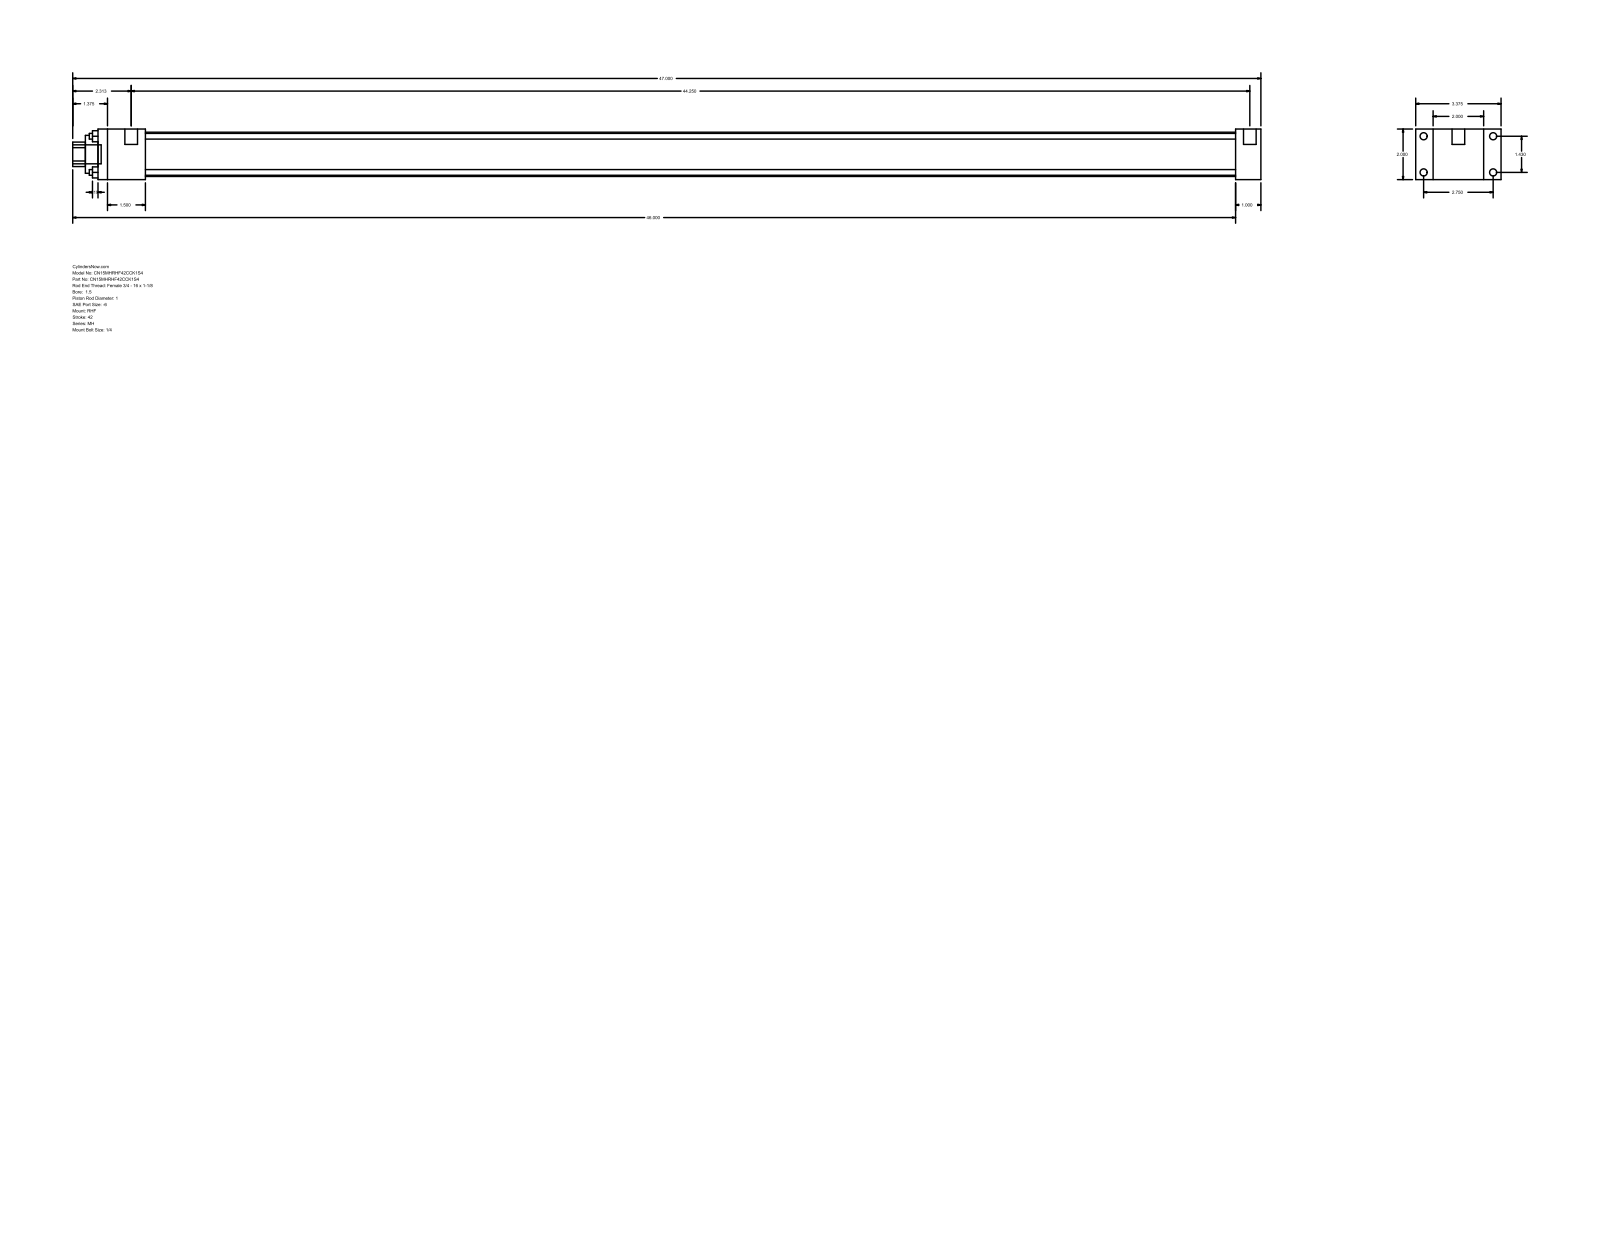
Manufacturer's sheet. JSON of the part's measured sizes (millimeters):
{"part_name": "MH_RHF__0150_1", "step_written_by": "GSSL Pune (CONFIG_CONTROL_DESIGN)", "units": "millimeters", "bodies": {"solids": 0, "faces": 88, "planar": 60, "cylindrical": 28, "other": 0}, "overall_size": [1193.8, 85.72, 50.8], "round_holes": [[5.71, 4], [25.4, 1], [38.1, 1], [44.45, 1]], "round_bosses_or_shafts": [[7.14, 4], [5.56, 4], [12.7, 2], [19.05, 1]], "partial_cylinders_radius": [[12.29, 1]], "face_to_face_distances": [50.8, 25.4, 17.46, 68.26, 85.72, 1168.4, 1143, 47.63, 1095.37, 1120.77], "hole_center_spacings": [25.68, 36.32, 51.36]}
